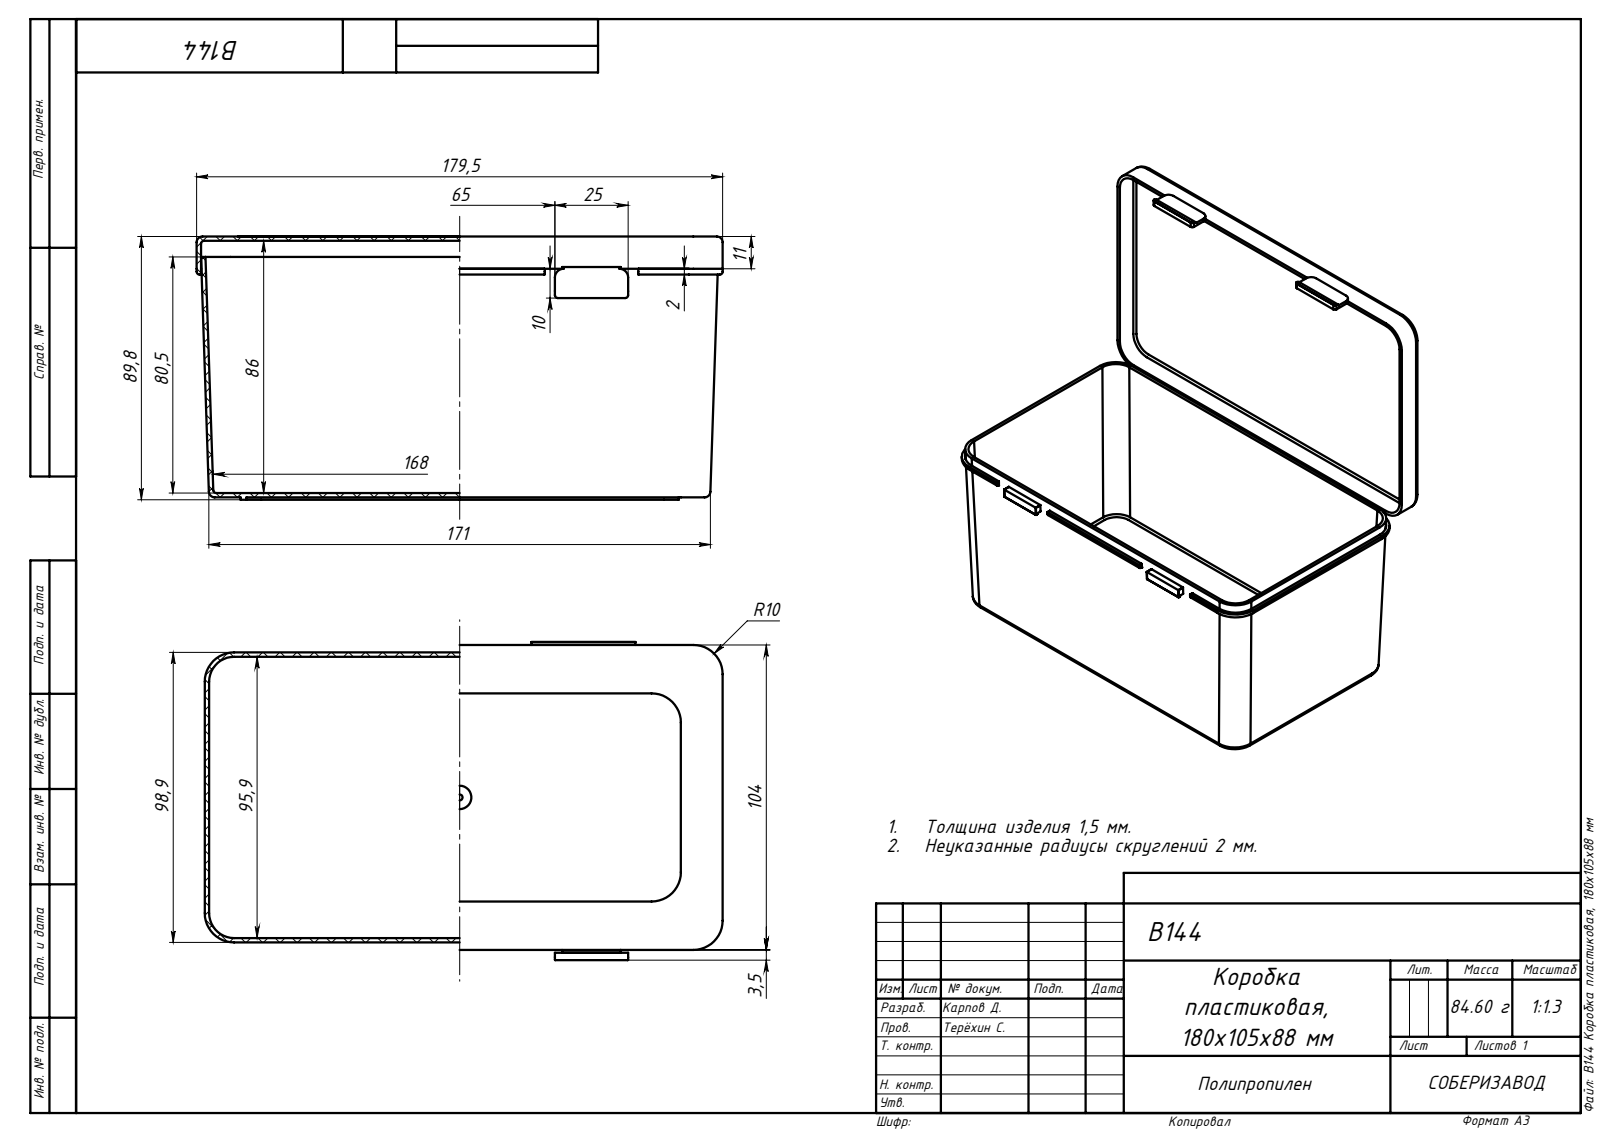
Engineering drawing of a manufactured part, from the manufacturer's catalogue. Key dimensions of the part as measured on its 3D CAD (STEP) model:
Part name (STEP PRODUCT): B144 Емкость; B144 Крышка; B144 Защелка; B144 Коробка пластиковая, 180x105x88 мм
STEP written by: SolidWorks 2020 (AUTOMOTIVE_DESIGN)
Units: millimetres
Bodies: 6 solids, 322 faces (133 planar, 125 cylindrical, 64 other)
Overall size (bounding box): 179.5 × 108.5 × 89.8
Volume: 125 542 mm³ · Surface area: 171 260 mm²
Round bosses / shafts (diameter × count): ⌀2 ×1
Partial cylindrical surfaces — rounded edges, fillets, slot ends (radius × count): R0.1 ×47, R1 ×16, R10 ×12, R2 ×9, R5 ×8, R8.5 ×8, R3 ×4
Main face-to-face distances: 1.5, 87.5, 86, 88.9, 87.4, 1.4, 89, 102.5, 78, 76.5
